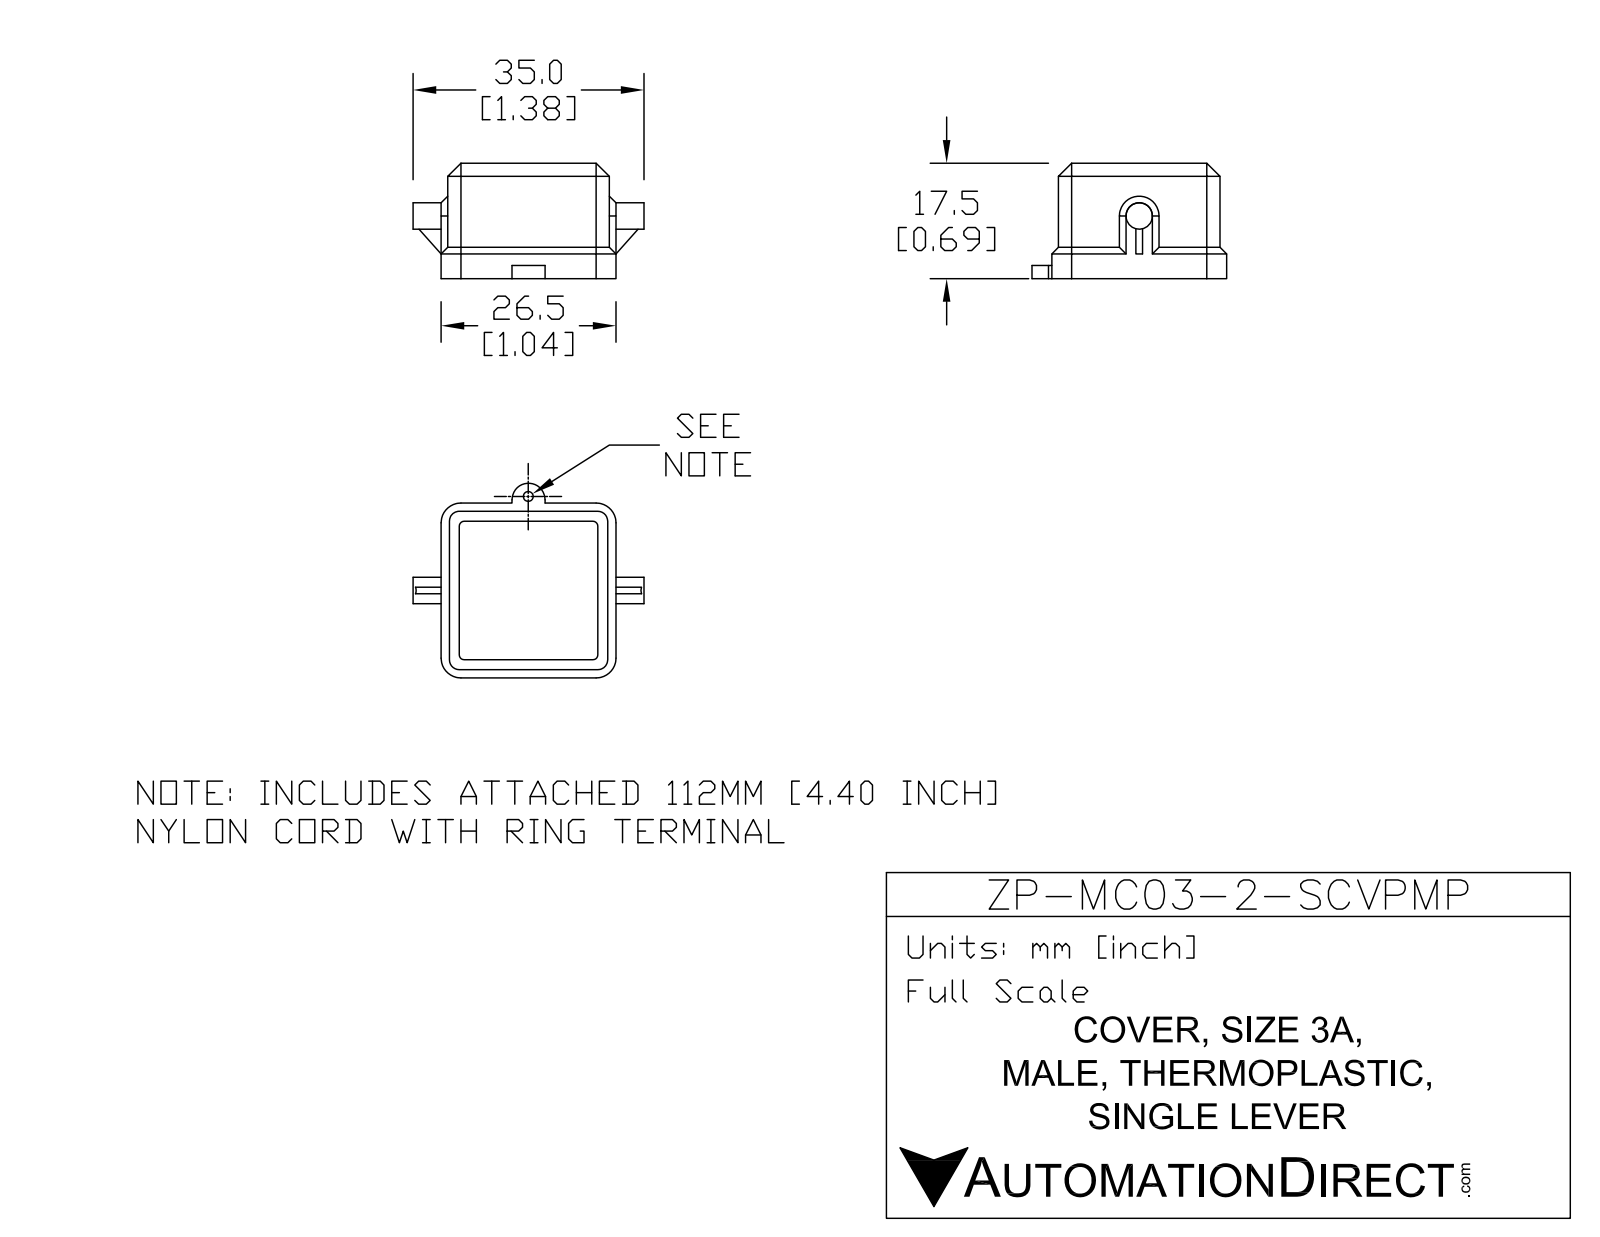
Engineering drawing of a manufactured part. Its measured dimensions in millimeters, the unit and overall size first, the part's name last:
Units: millimetres
Overall size (bounding box): 35 × 29.5 × 17.5
Round holes (diameter × count): ⌀1.5 ×1
Round bosses / shafts (diameter × count): ⌀4 ×1
Partial cylindrical surfaces — rounded edges, fillets, slot ends (radius × count): R0.75 ×4, R1.5 ×4, R2 ×4, R3 ×4, R2.5 ×1
Main face-to-face distances: 1.75, 22.75, 21, 2, 24.5, 1, 2.75, 23.75, 25.5, 1.5
Volume: 3 596 mm³ · Surface area: 4 395 mm²
Bodies: 1 solid, 75 faces (45 planar, 20 cylindrical, 10 other)
Part name (STEP PRODUCT): ZP-MC03A-2-SCVPMP
STEP written by: SolidWorks 2011 (AUTOMOTIVE_DESIGN)
